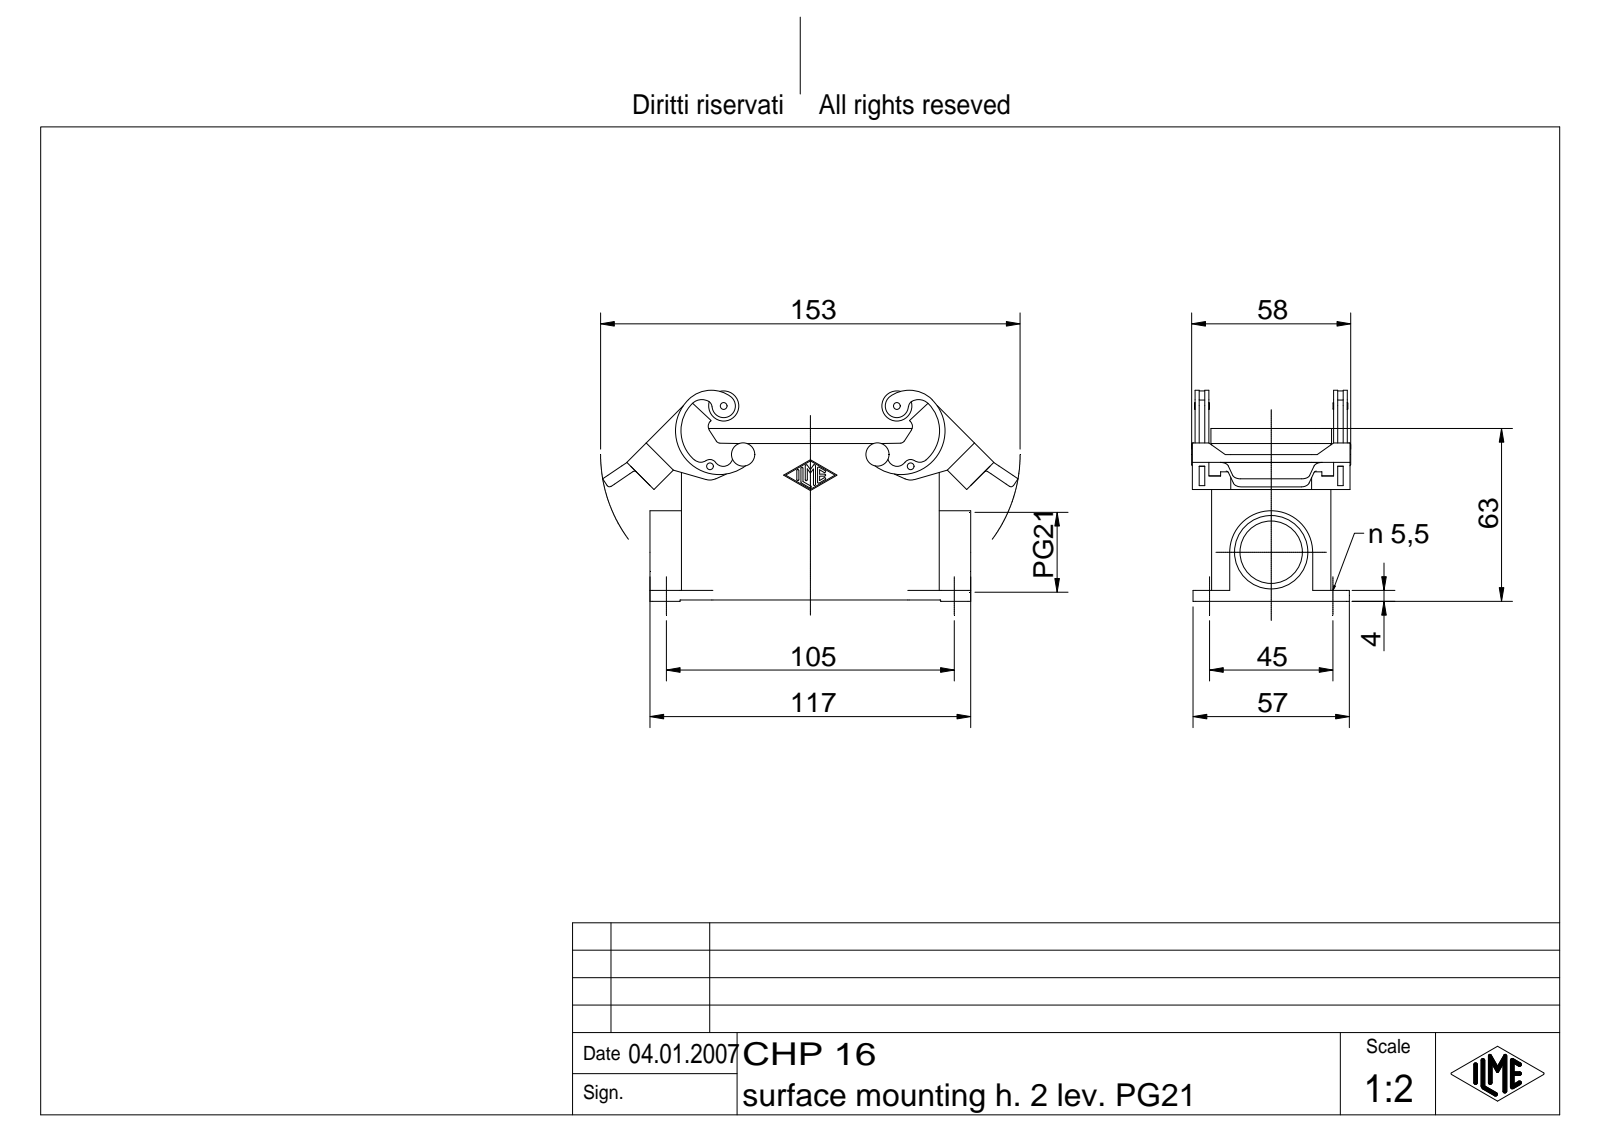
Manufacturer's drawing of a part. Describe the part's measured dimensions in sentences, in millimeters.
The part is named "CHP 16". Its 3-D file was written by "Autodesk Inventor 7 (AUTOMOTIVE_DESIGN)". It is 1 solid with 749 faces: 191 planar, 205 cylindrical and 353 other. Overall it measures 151.49 by 76.94 by 58 millimeters. Its volume is 106 794 cubic millimeters and its surface area 62 172 square millimeters. Round holes: 4 of diameter 2, 4 of diameter 5.5, 2 of diameter 2.5, 1 of diameter 22.78, 1 of diameter 26.78. Round bosses or shafts: 2 of diameter 11, 2 of diameter 5, 2 of diameter 3. Partial cylindrical surfaces (rounded edges, fillets, slot ends): 20 of radius 1, 14 of radius 0.38, 12 of radius 3, 8 of radius 6, 6 of radius 2.5, 4 of radius 1.5, 4 of radius 2, 4 of radius 3.5. The main face-to-face distances are 3, 40.5, 43.5, 3.5, 37.5, 4, 50.5, 0.75, 40.75, 4.5. The hole center spacings are 22.56, 45, 71.62, 105, 114.24, 63.14, 73.18.
